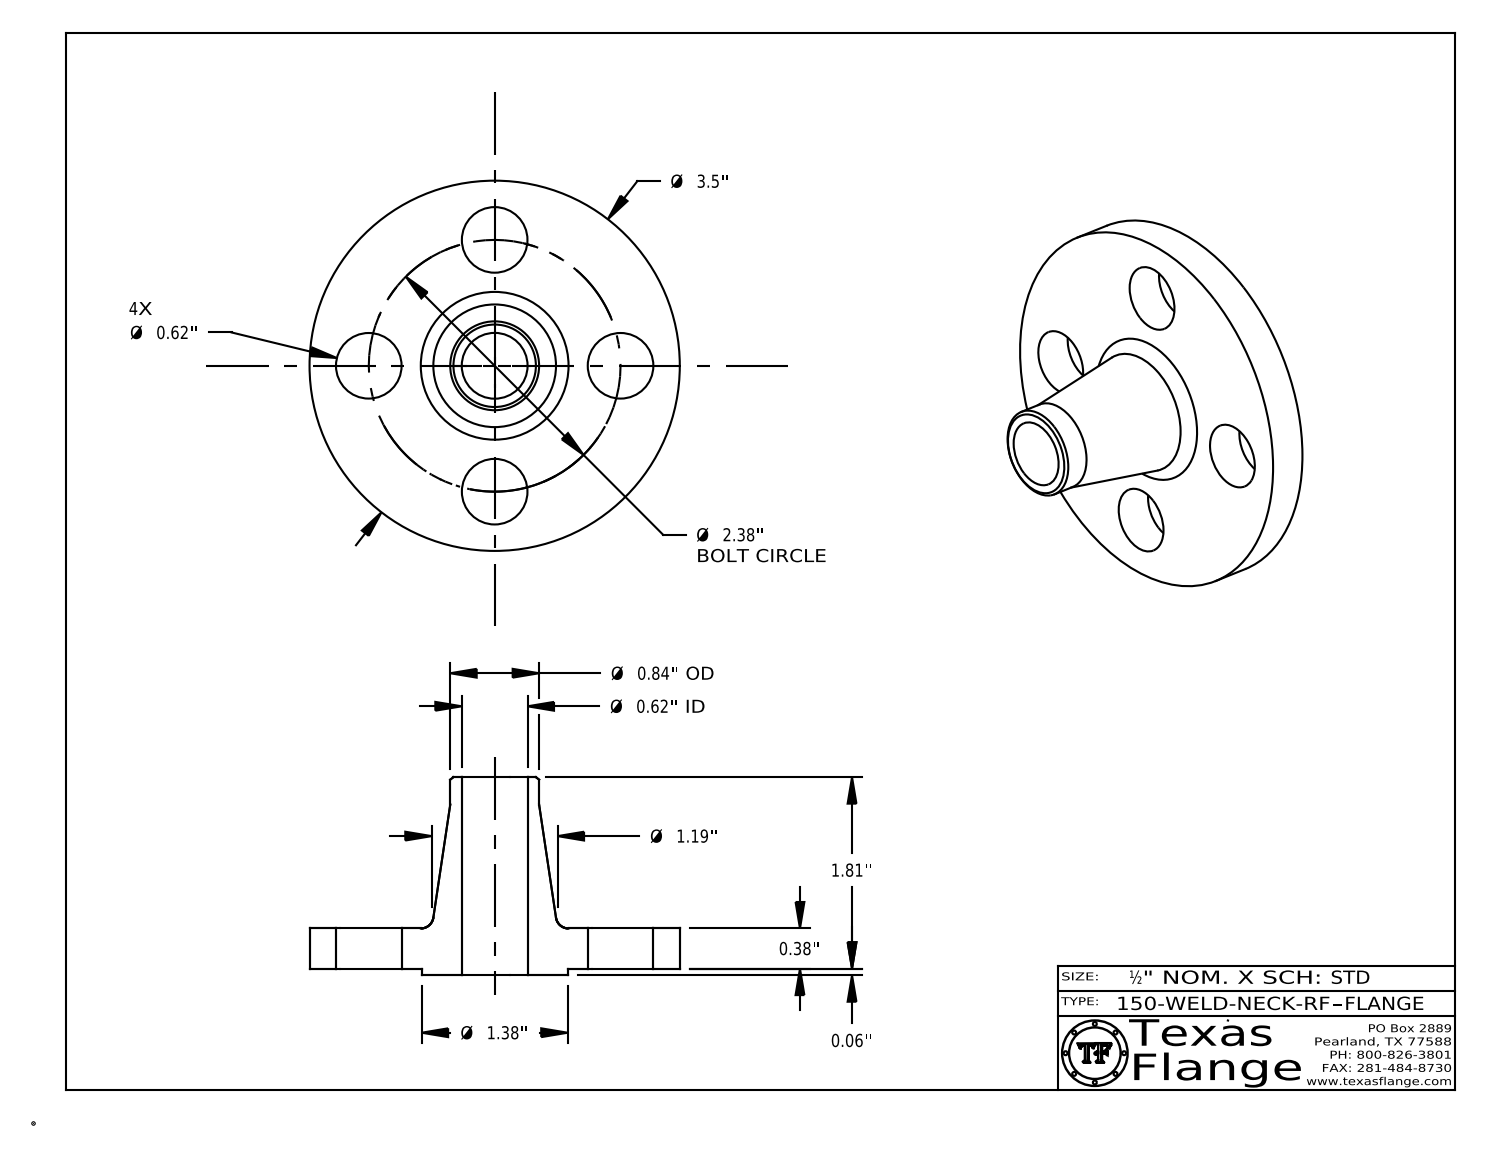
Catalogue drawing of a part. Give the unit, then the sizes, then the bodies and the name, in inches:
Units: inches
Overall size (bounding box): 3.5 × 3.5 × 1.873
Round holes (diameter × count): ⌀0.62 ×4, ⌀0.495 ×1, ⌀0.622 ×1
Round bosses / shafts (diameter × count): ⌀0.03 ×8, ⌀3.5 ×1, ⌀1.38 ×1, ⌀0.84 ×1, ⌀0.39 ×1
Main face-to-face distances: 0.38, 0.063, 0.443, 1.872, 1.81, 1.43, 0.428, 0.365, 0.015, 1.445
Hole centre spacings: 1.19, 1.683, 0.911, 2.199, 2.38, 1.19
Volume: 3.828 in³ · Surface area: 31.11 in²
Bodies: 1 solid, 411 faces (369 planar, 36 cylindrical, 6 other)
Part name (STEP PRODUCT): 150-WELD-NECK-RF
STEP written by: CATIA V5 STEP AP214 (AUTOMOTIVE_DESIGN)
